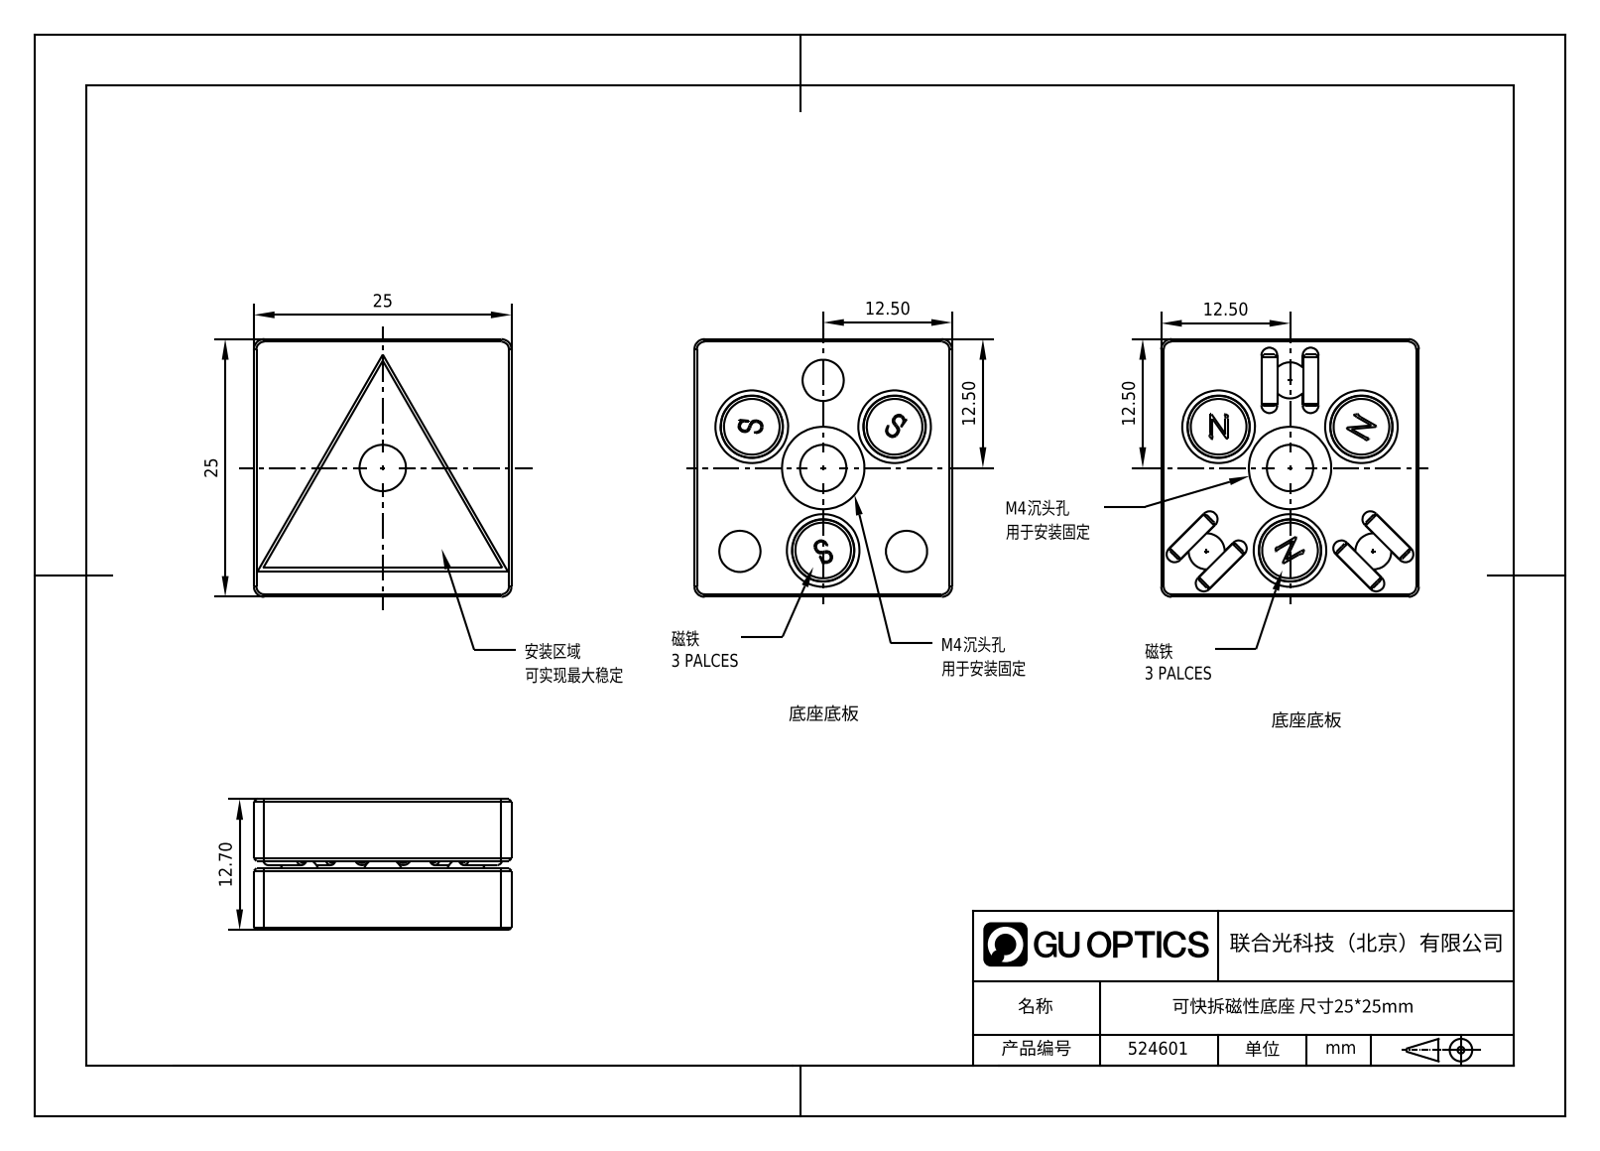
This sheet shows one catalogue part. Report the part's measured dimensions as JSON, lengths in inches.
{"part_name": "1.4.6.36，ZGD-K25，可调光学接杆底座，尺寸25mmx25mm，带M4沉头孔，A", "step_written_by": "SolidWorks 2018 (CONFIG_CONTROL_DESIGN)", "units": "inches", "bodies": {"solids": 0, "faces": 104, "planar": 46, "cylindrical": 34, "other": 24}, "overall_size": [0.984, 0.984, 0.5], "round_holes": [[0.177, 1], [0.315, 1]], "round_bosses_or_shafts": [[0.059, 4]], "partial_cylinders_radius": [[0.031, 6], [0.039, 4]], "face_to_face_distances": [0.236, 0.264, 0.5, 0.984, 0.028, 0.187, 0.849, 1.035, 0.662, 0.499]}
